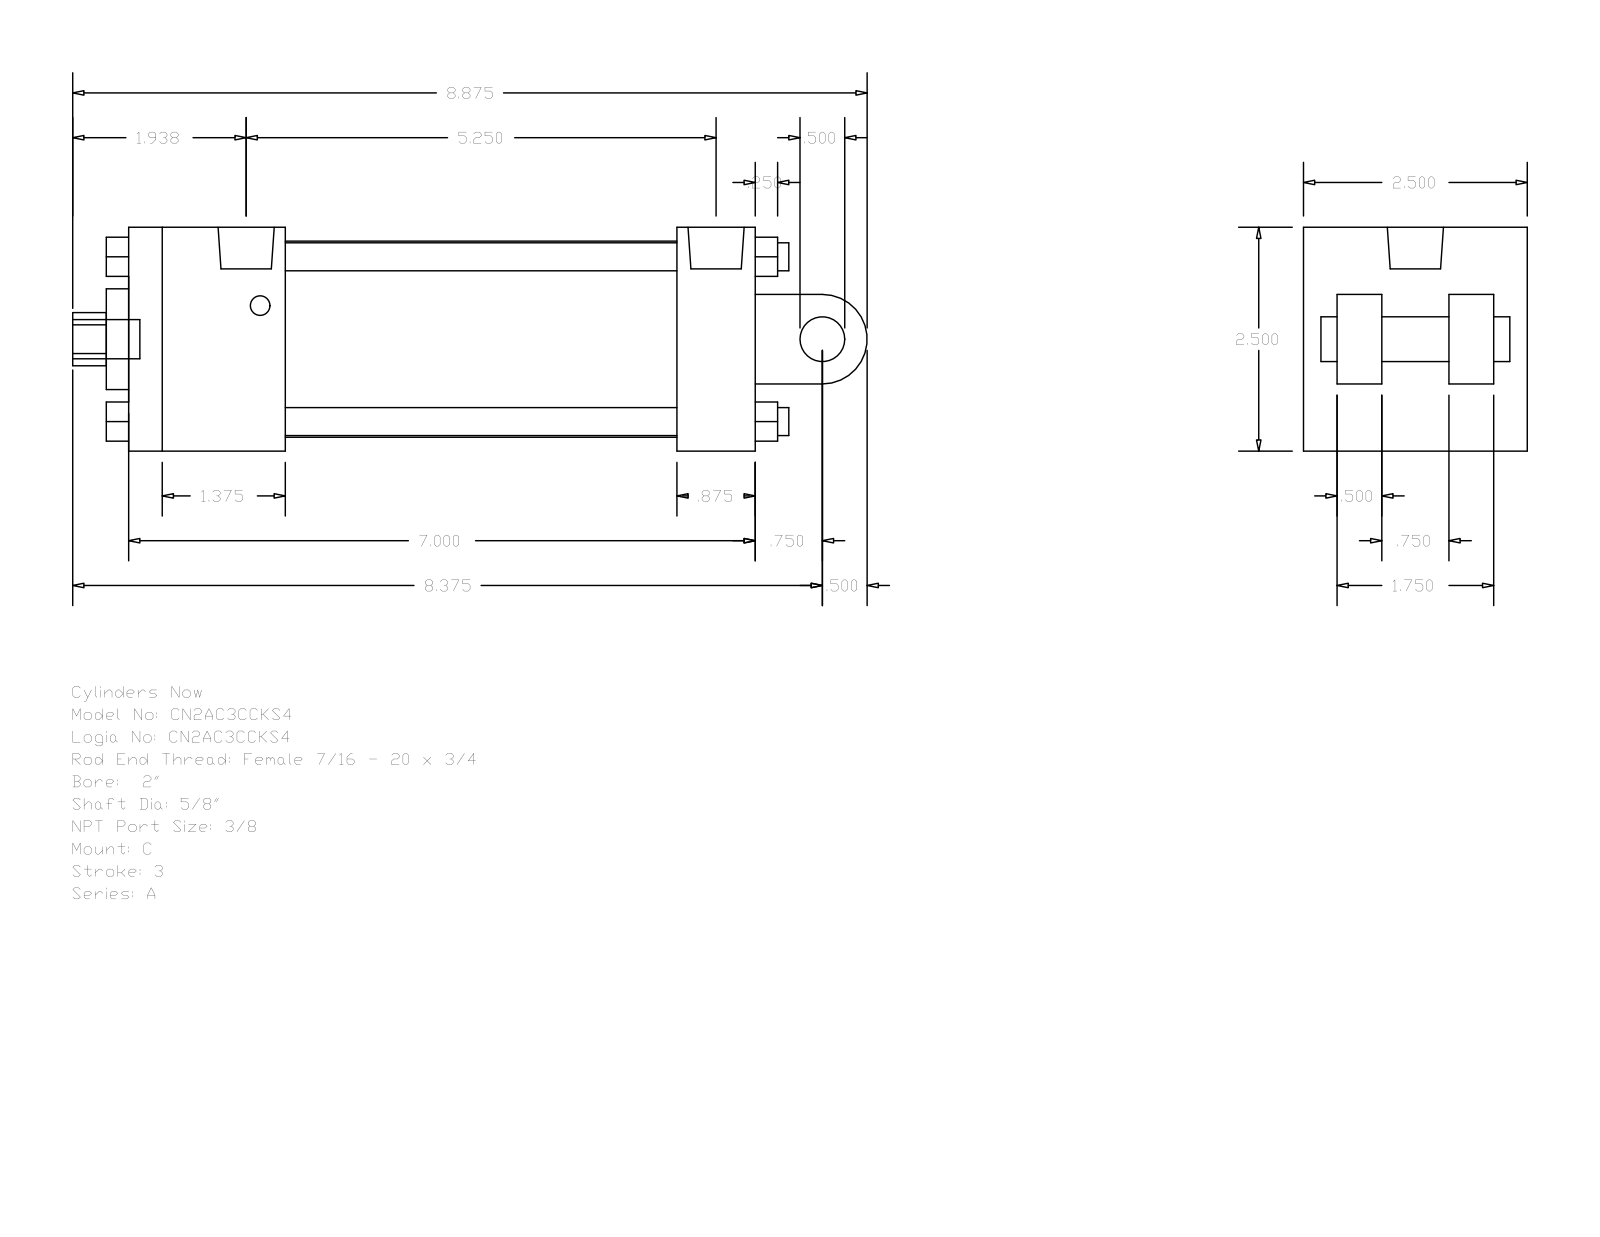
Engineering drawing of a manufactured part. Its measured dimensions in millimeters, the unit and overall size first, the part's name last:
Units: millimetres
Overall size (bounding box): 225.43 × 63.5 × 63.5
Round holes (diameter × count): ⌀5.56 ×2, ⌀15.88 ×1, ⌀15.93 ×1, ⌀28.57 ×1, ⌀55.63 ×1
Round bosses / shafts (diameter × count): ⌀7.94 ×4, ⌀5.56 ×2, ⌀15.93 ×1, ⌀12.7 ×1, ⌀11.11 ×1
Partial cylindrical surfaces — rounded edges, fillets, slot ends (radius × count): R7.54 ×1, R12.7 ×1
Main face-to-face distances: 63.5, 177.8, 44.45, 9.52, 133.35, 155.57, 111.12, 22.23, 12.7, 41.28
Hole centre spacings: 3.97
Bodies: 0 solids, 135 faces (102 planar, 33 cylindrical, 0 other)
Part name (STEP PRODUCT): A_C__0200_0.625
STEP written by: GSSL Pune (CONFIG_CONTROL_DESIGN)
